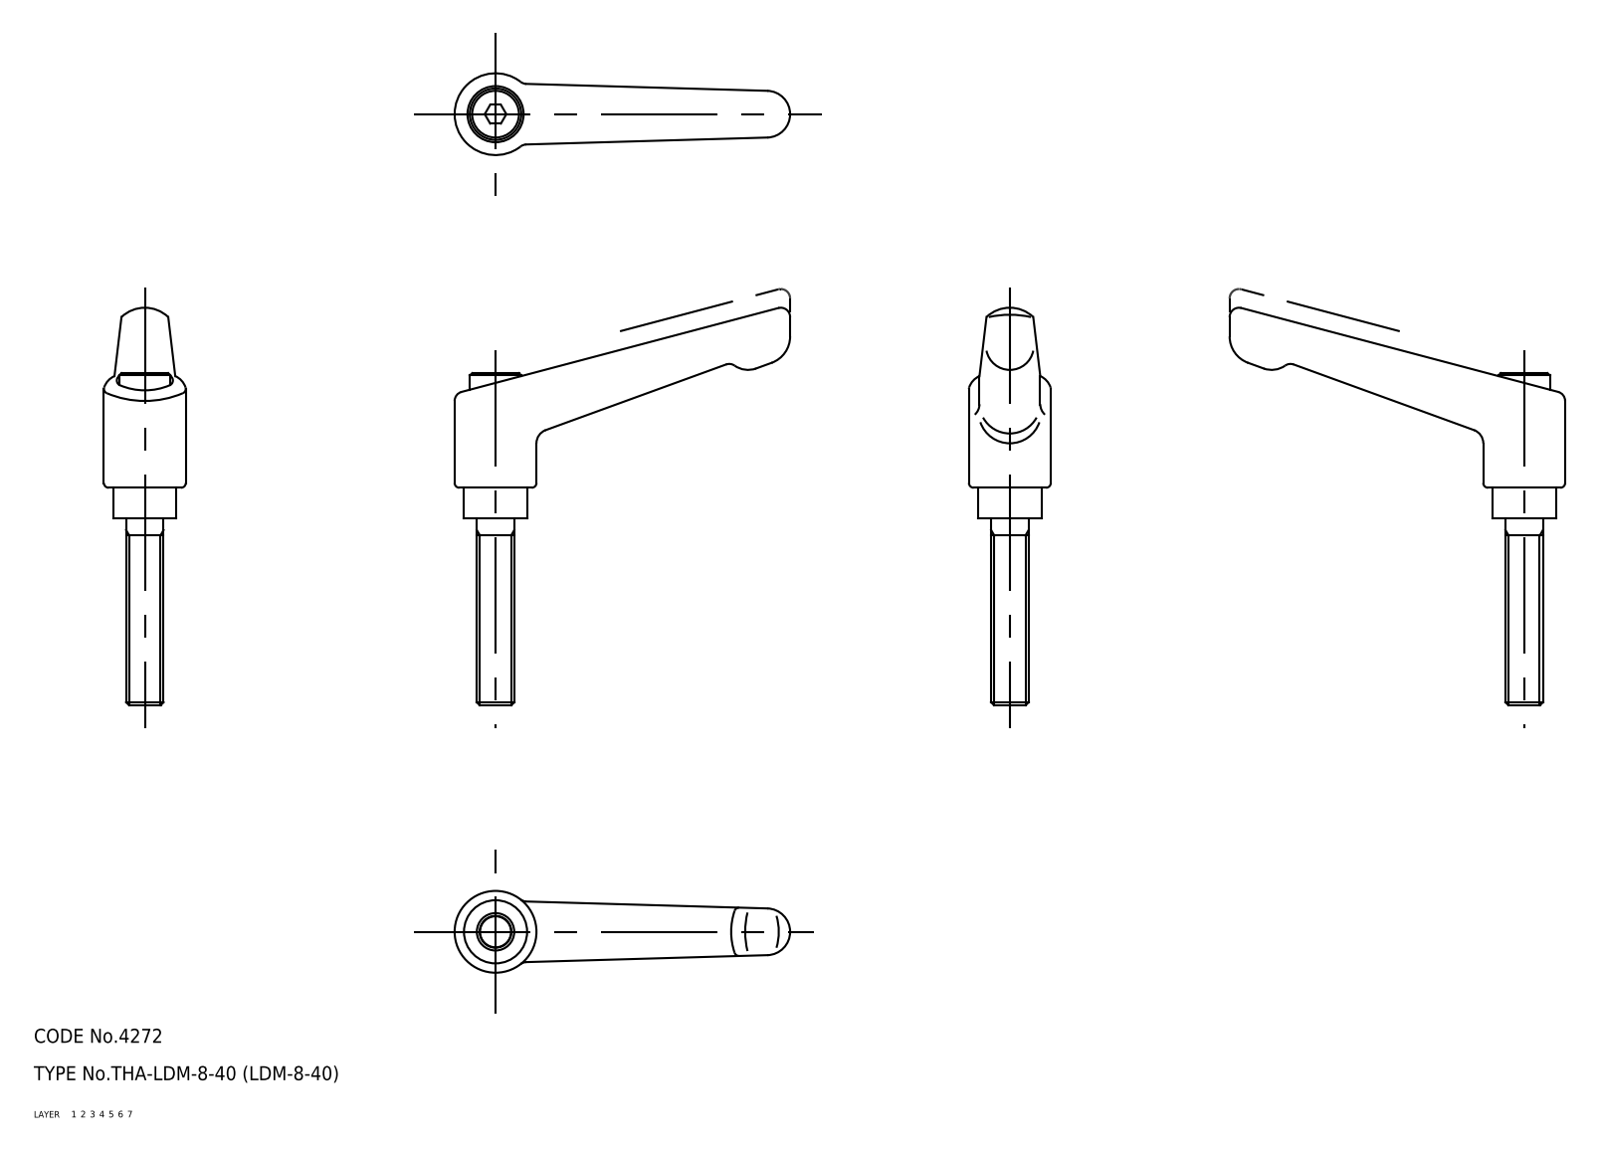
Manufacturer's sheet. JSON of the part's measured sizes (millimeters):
{"part_name": "sleeve; screw; handle; LDM_8_40_26492_36", "step_written_by": "CADfix (AUTOMOTIVE_DESIGN)", "units": "millimeters", "bodies": {"solids": 3, "faces": 75, "planar": 0, "cylindrical": 0, "other": 75}, "overall_size": [85, 71.75, 17.5], "volume_mm3": 14123, "surface_area_mm2": 7020}
